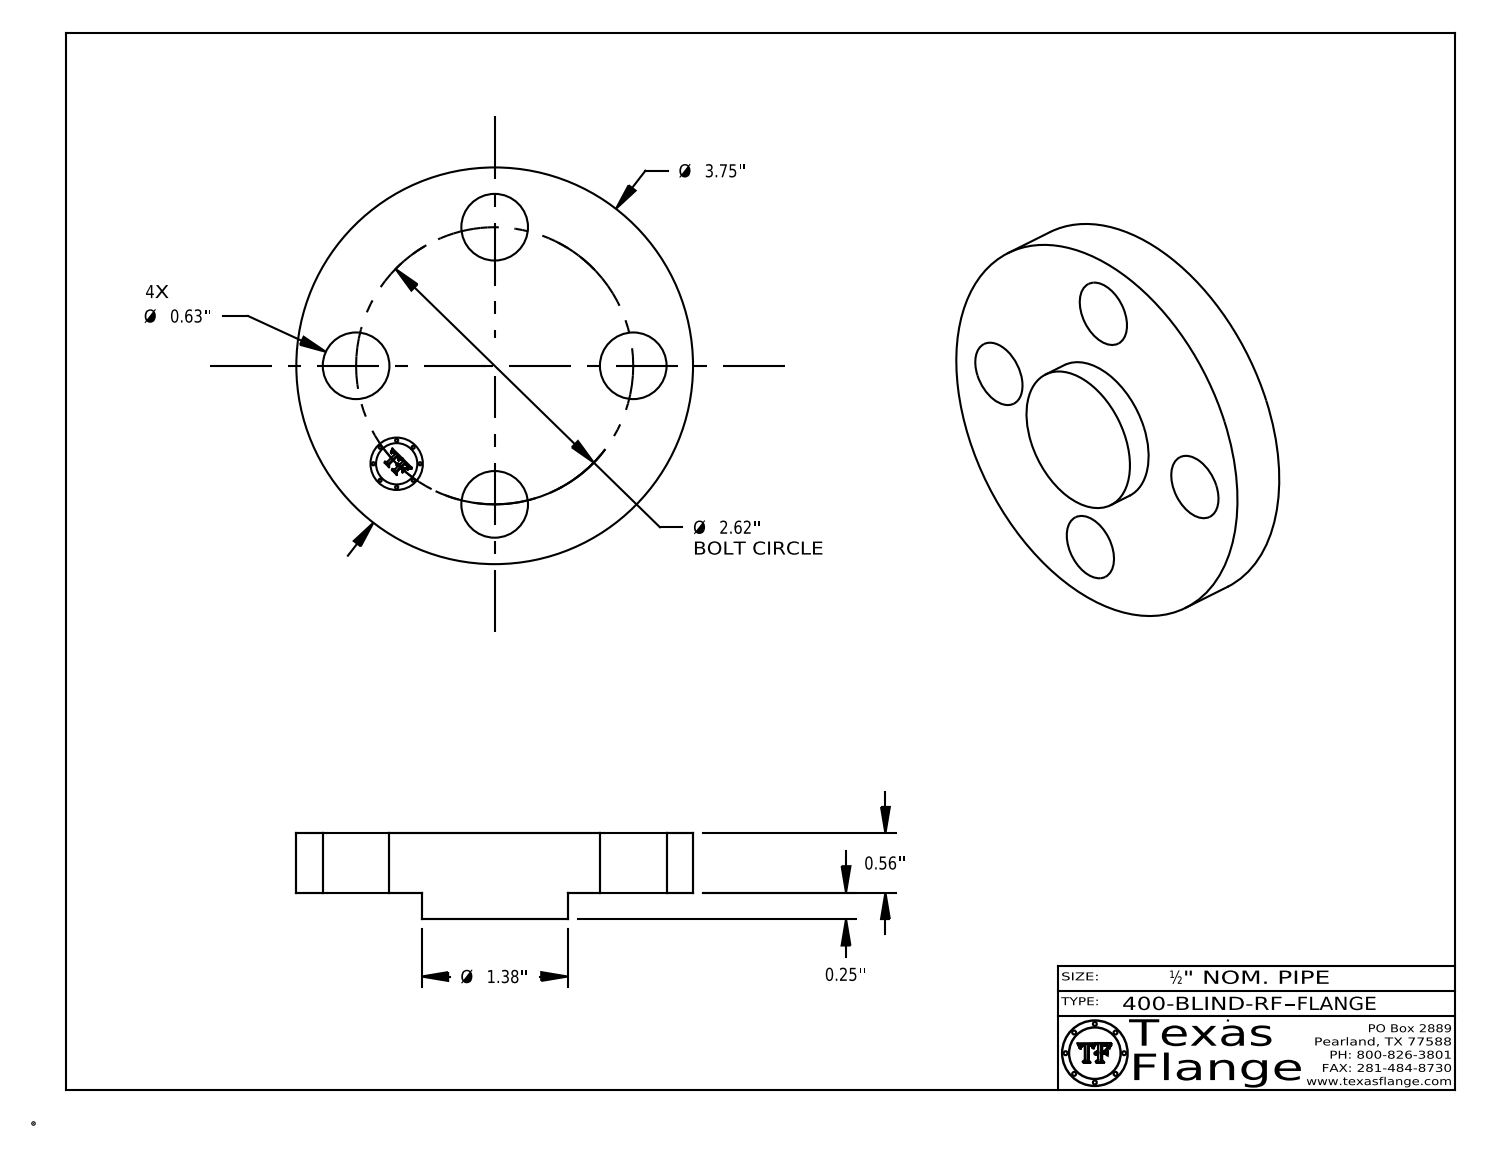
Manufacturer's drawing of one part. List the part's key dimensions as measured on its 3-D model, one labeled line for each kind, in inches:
Part name (STEP PRODUCT): 400-BLIND-RF
STEP written by: CATIA V5 STEP AP214 (AUTOMOTIVE_DESIGN)
Units: inches
Bodies: 1 solid, 400 faces (368 planar, 32 cylindrical, 0 other)
Overall size (bounding box): 3.75 × 3.75 × 0.81
Volume: 5.859 in³ · Surface area: 31.8 in²
Round holes (diameter × count): ⌀0.63 ×4, ⌀0.495 ×1
Round bosses / shafts (diameter × count): ⌀0.03 ×8, ⌀3.75 ×1, ⌀1.38 ×1, ⌀0.39 ×1
Main face-to-face distances: 0.56, 0.25, 0.81, 0.795, 0.545, 0.015, 0.148, 0.144, 0.027, 0.096
Hole centre spacings: 1.852, 1.003, 2.42, 2.62
